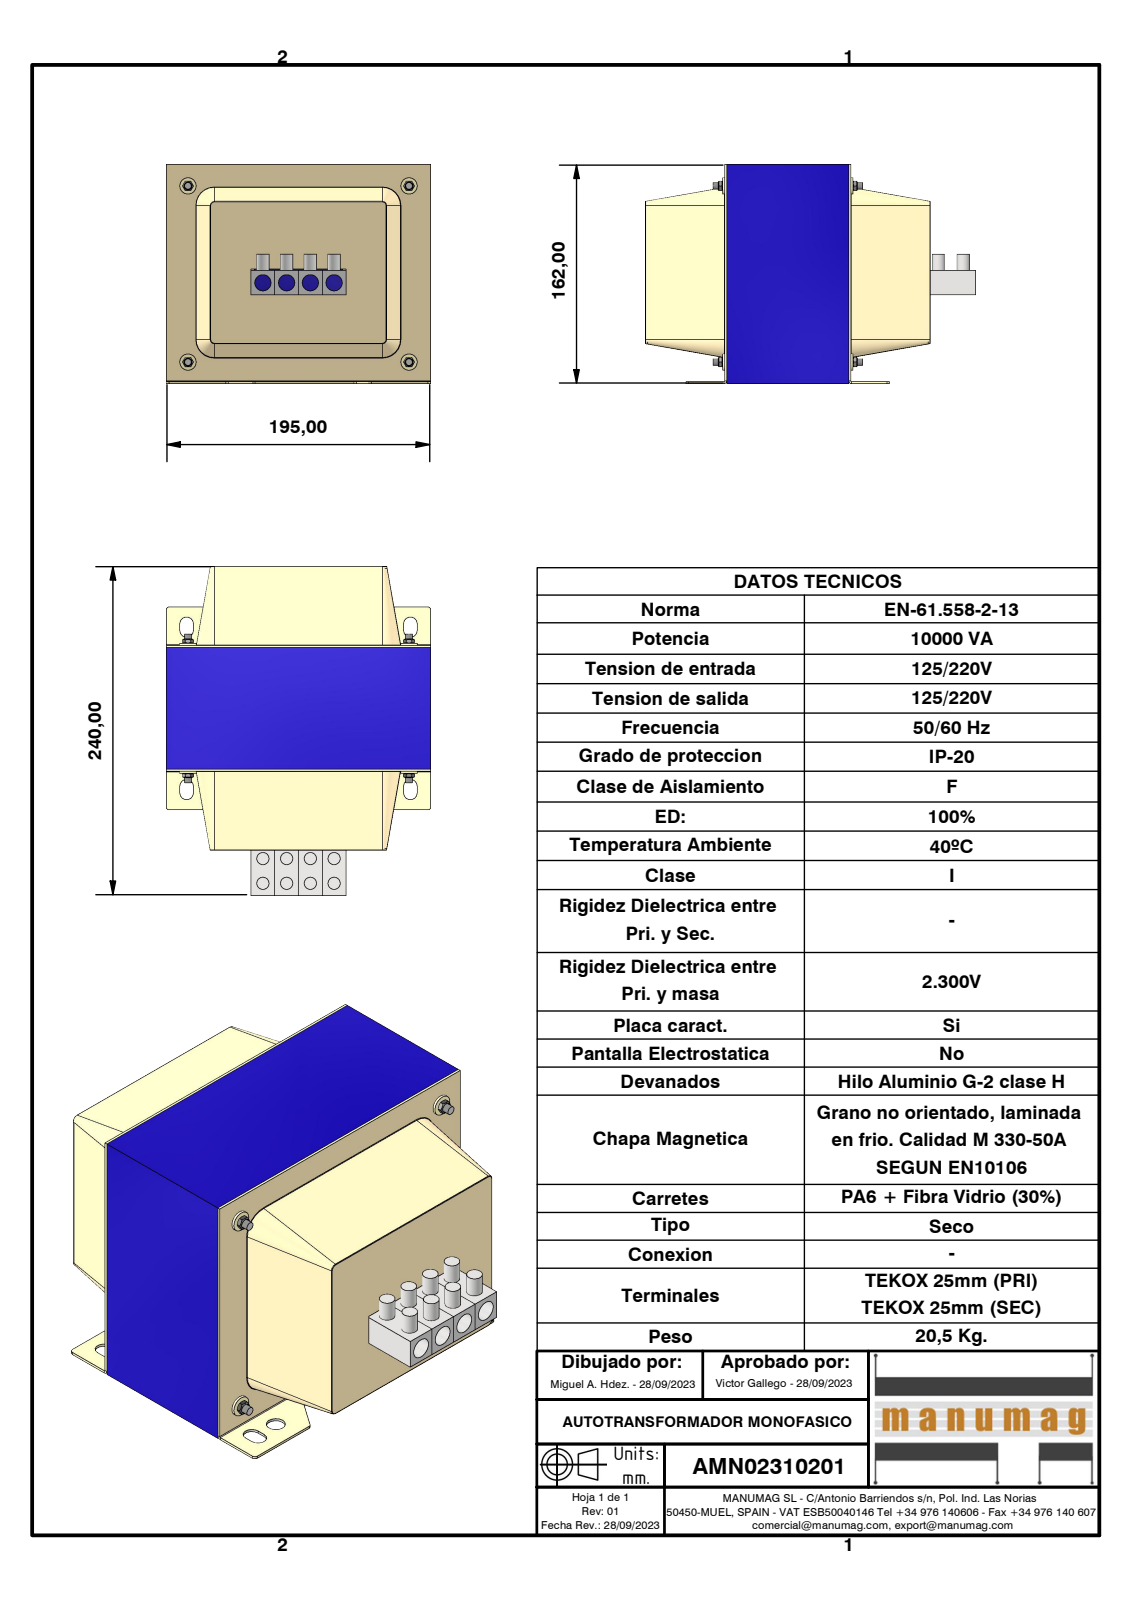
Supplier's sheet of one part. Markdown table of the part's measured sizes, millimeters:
| quantity | value |
| --- | --- |
| part name | AMN02310201; EI195 x 162 - 90 (Rc65) Azul; TAPA RC65 VENTANA 4 ELEMENTOS 25; TAPA RC65 CIEGA (+5 more) |
| STEP written by | Autodesk Inventor 2023 (AUTOMOTIVE_DESIGN) |
| units | millimeters |
| bodies | 27 solids, 374 faces (198 planar, 104 cylindrical, 72 other) |
| overall size | 243.5 × 195 × 162 |
| volume | 2 380 000 mm³ |
| surface area | 438 525 mm² |
| round holes (diameter × count) | 11 × 8, 3.24 × 4, 5 × 4, 9 × 4, 12 × 4 |
| round bosses / shafts (diameter × count) | 9 × 8, 12 × 4, 5.9 × 4 |
| partial cylindrical surfaces (radius × count) | 0.38 × 16, 2 × 14, 5 × 8, 0.5 × 2 |
| main face-to-face distances | 1.5, 58.5, 150, 130, 32.5, 90, 65, 148.5, 60, 57 |
| hole center spacings | 17.5, 35, 80.47, 90.36, 93.35, 102, 107.55, 115.14 |
